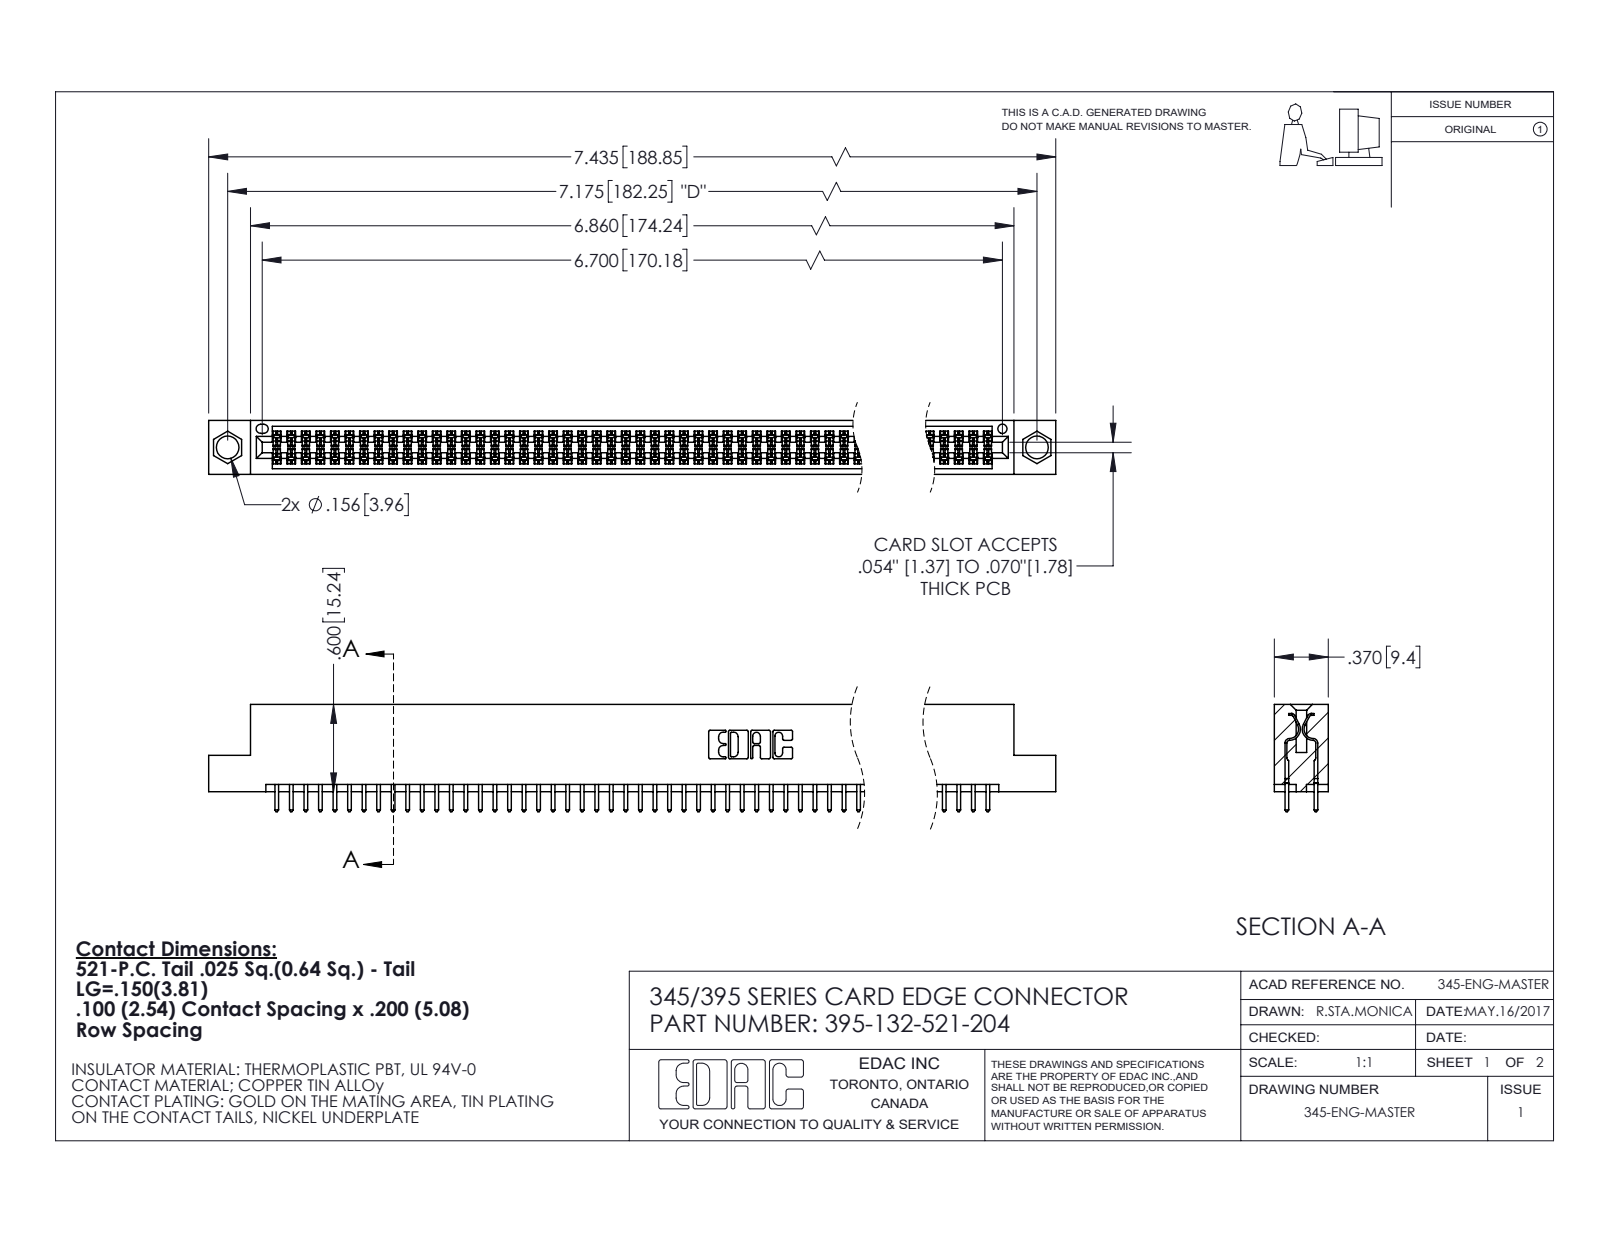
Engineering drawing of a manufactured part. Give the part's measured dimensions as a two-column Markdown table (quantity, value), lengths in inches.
| quantity | value |
| --- | --- |
| part name | 345-292-001_345-293-121; 395-132-521-204; 345 Part_Flush Mounting Lugs - 0.156 Dia-TI |
| STEP written by | SolidWorks 2020 (CONFIG_CONTROL_DESIGN) |
| units | inches |
| bodies | 133 solids, 6740 faces (4450 planar, 2290 cylindrical, 0 other) |
| overall size | 7.435 × 0.737 × 0.37 |
| volume | 1.123 in³ |
| surface area | 42.12 in² |
| round holes (diameter × count) | 0.156 × 2, 0.064 × 1 |
| partial cylindrical surfaces (radius × count) | 0.006 × 263, 0.01 × 132, 0.01 × 22, 0.007 × 6, 0.031 × 6, 0.026 × 3, 0.014 × 2, 0.019 × 2 |
| main face-to-face distances | 0.072, 0.298, 0.2, 0.098, 0.272, 0.025, 0.37, 0.225, 0.175, 0.149 |
| hole center spacings | 0.27, 6.939, 7.175 |
